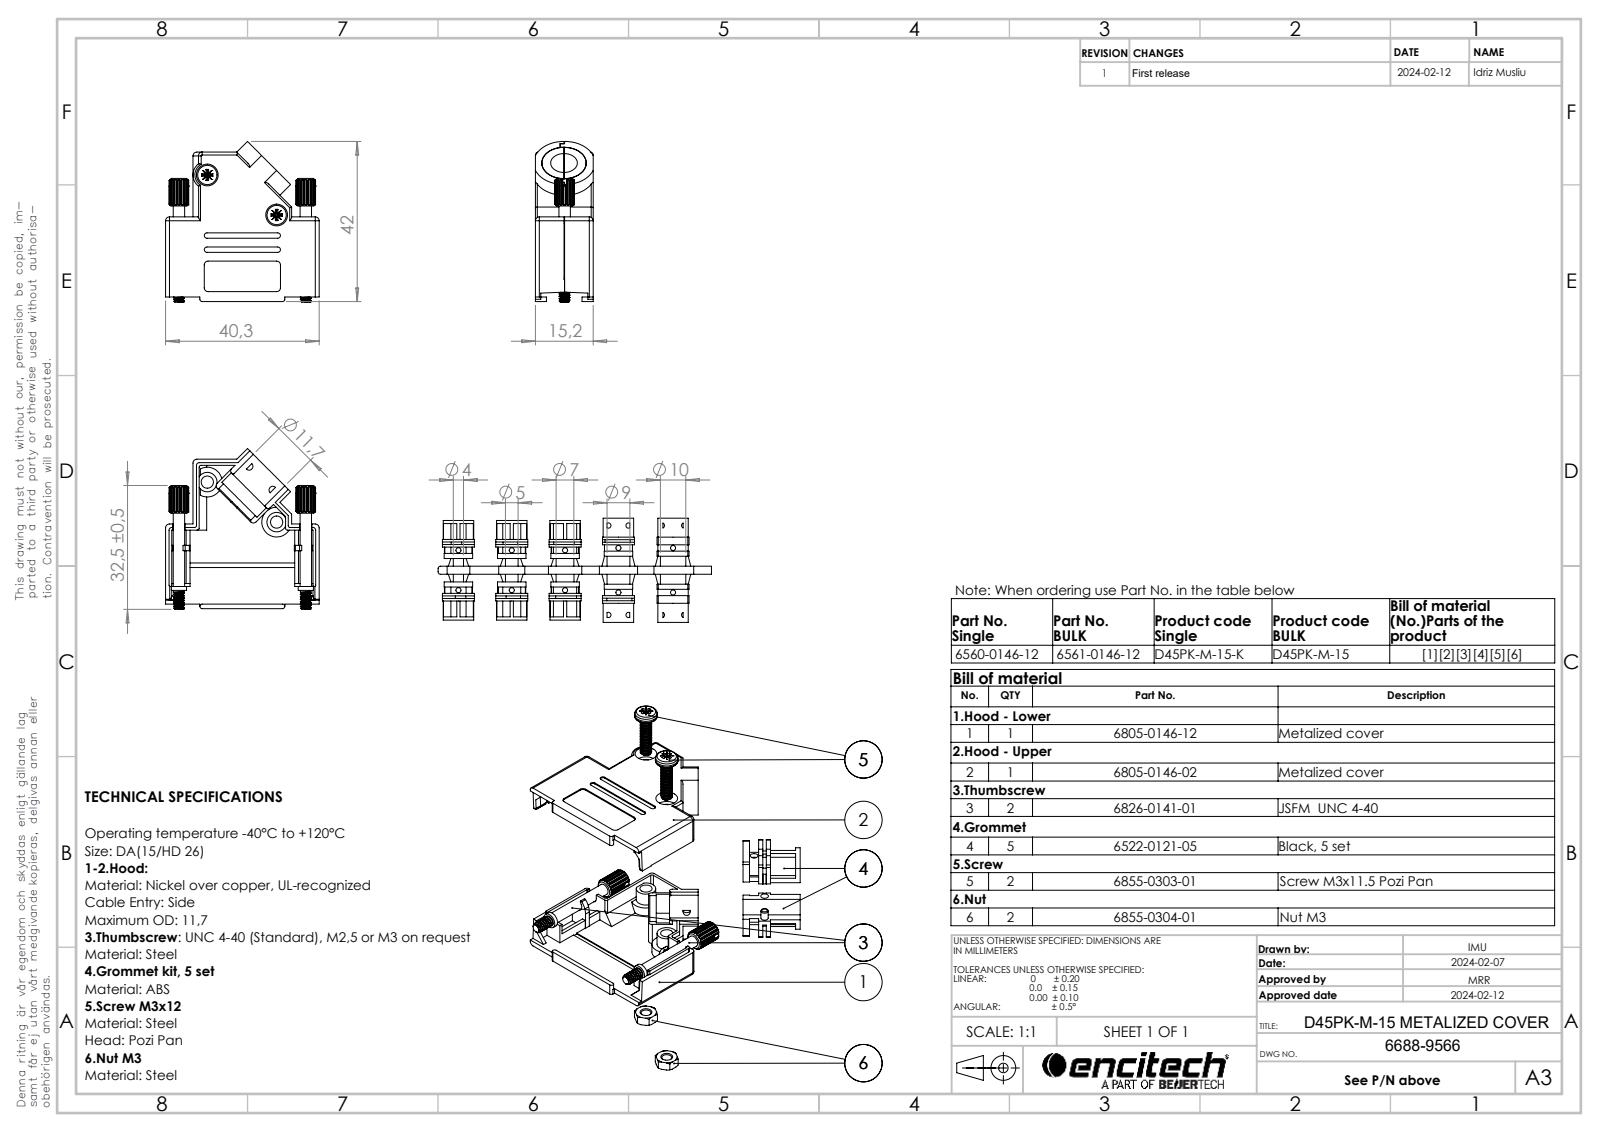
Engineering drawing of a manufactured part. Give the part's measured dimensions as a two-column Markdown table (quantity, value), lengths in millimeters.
| quantity | value |
| --- | --- |
| part name | 6826-0141-01; 6805-0146-02; Assembly of 6560-0146-12; 6855-0304-01 (+3 more) |
| STEP written by | SolidWorks 2021 (AUTOMOTIVE_DESIGN) |
| units | millimeters |
| bodies | 10 solids, 925 faces (548 planar, 265 cylindrical, 112 other) |
| overall size | 42.2 × 40.3 × 15.15 |
| volume | 7 984 mm³ |
| surface area | 12 771 mm² |
| round holes (diameter × count) | 2 × 3, 2.6 × 2, 3.2 × 2, 5.7 × 2, 7 × 1, 11.7 × 1 |
| round bosses / shafts (diameter × count) | 5.1 × 2, 4 × 2, 3 × 2, 2.9 × 2, 2.8 × 2, 1.9 × 2, 11.6 × 1, 9.2 × 1 |
| partial cylindrical surfaces (radius × count) | 0.5 × 23, 1 × 19, 0.75 × 13, 0.1 × 8, 0.7 × 4, 1.6 × 4, 5.91 × 4, 0.33 × 2 |
| main face-to-face distances | 1.4, 13.75, 1.6, 15.15, 12.35, 7.2, 1.1, 7.5, 14.85, 13.45 |
| hole center spacings | 5.71, 6.06, 6.16, 9.37, 10, 11.71, 14.88, 16.1 |
